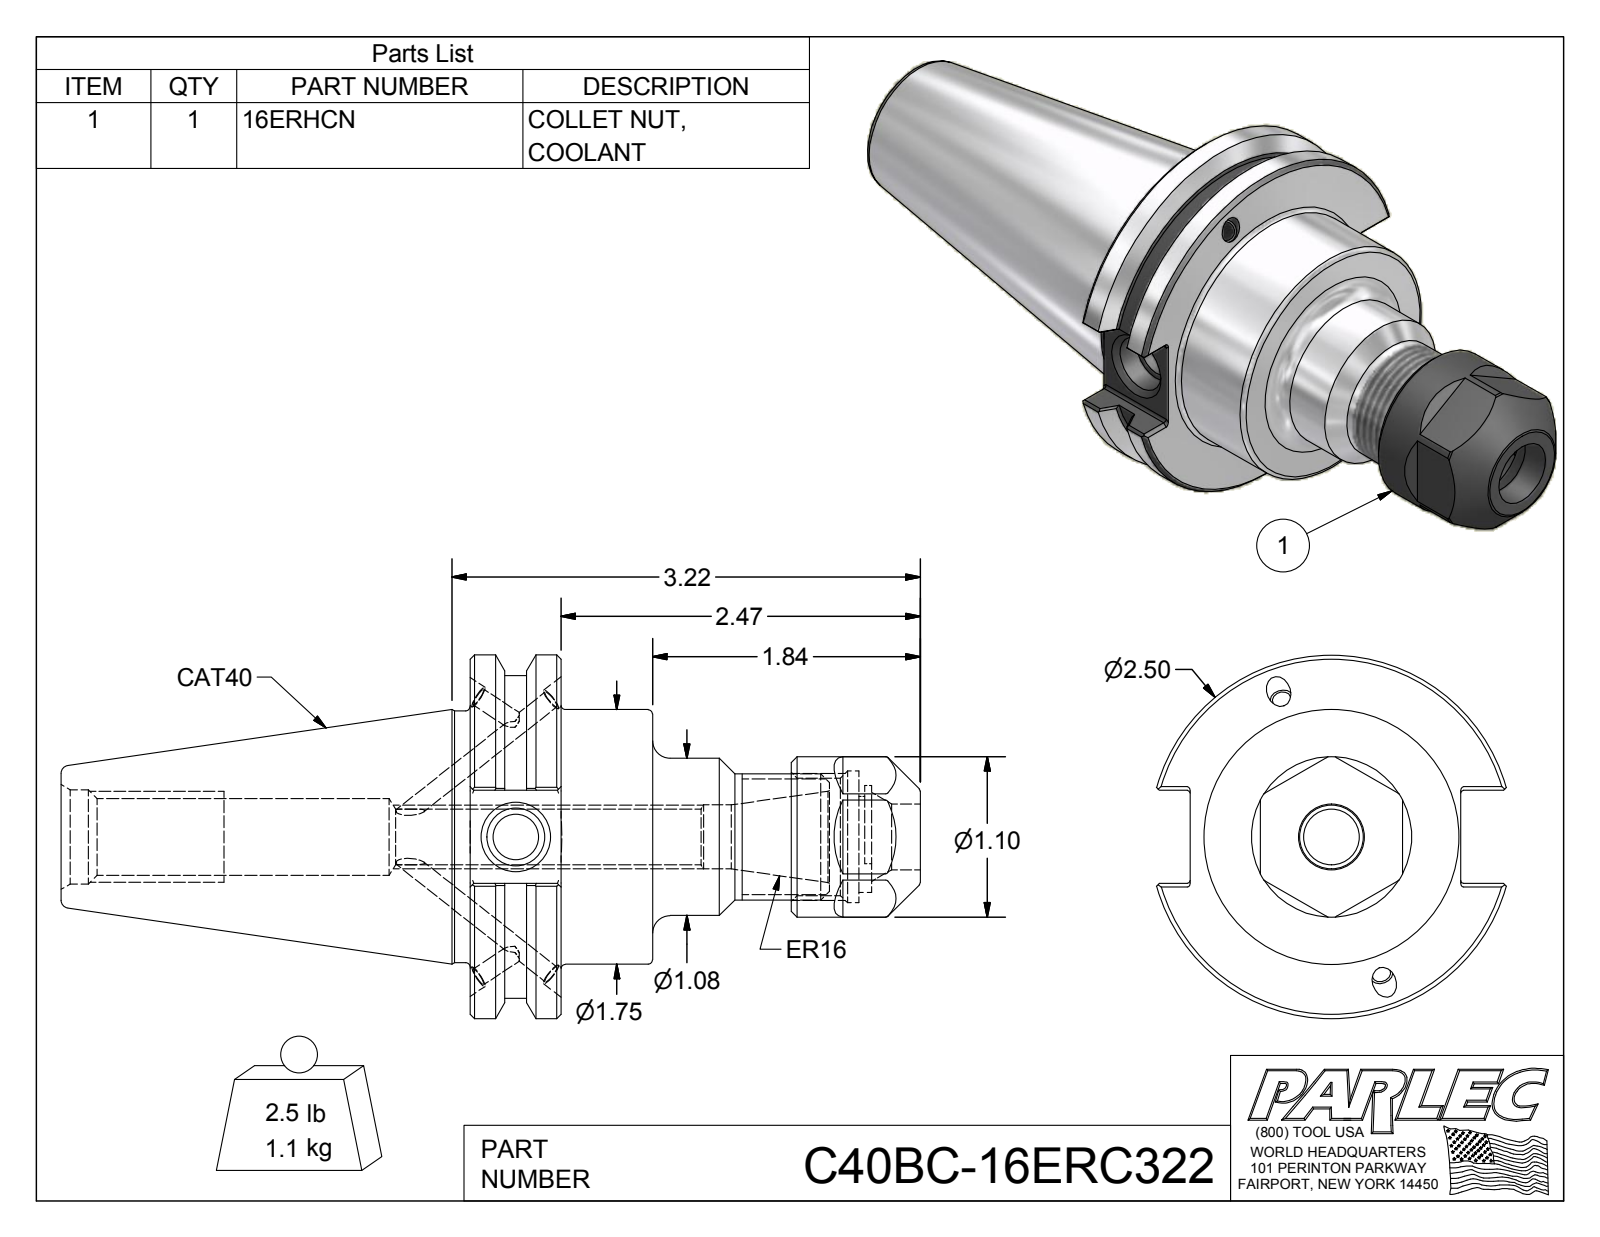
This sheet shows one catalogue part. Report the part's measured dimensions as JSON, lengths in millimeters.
{"part_name": "C40BCB-16ER3-1; 16ERHCN; 029-965; C40BC-16ERC322", "step_written_by": "Autodesk Inventor 2016 (AUTOMOTIVE_DESIGN)", "units": "millimeters", "bodies": {"solids": 6, "faces": 210, "planar": 93, "cylindrical": 54, "other": 63}, "overall_size": [150.04, 63.5, 61.11], "volume_mm3": 142454, "surface_area_mm2": 30891, "round_holes": [[3.3, 4], [4.1, 4], [8, 1], [9.73, 1], [10.13, 1], [11.18, 1], [11.5, 1], [13.39, 1], [16.46, 1], [16.8, 1], [20.5, 1], [23, 1]], "round_bosses_or_shafts": [[4.2, 4], [4, 4], [63.5, 1], [56.36, 1], [44.45, 1], [43.94, 1], [28, 1], [27.43, 1]], "partial_cylinders_radius": [[0.51, 12], [9, 1]], "face_to_face_distances": [15.88, 31.88, 16, 24.86, 67.92, 52.04, 36.04, 16.26, 56.12, 40.24], "hole_center_spacings": [1.3]}
